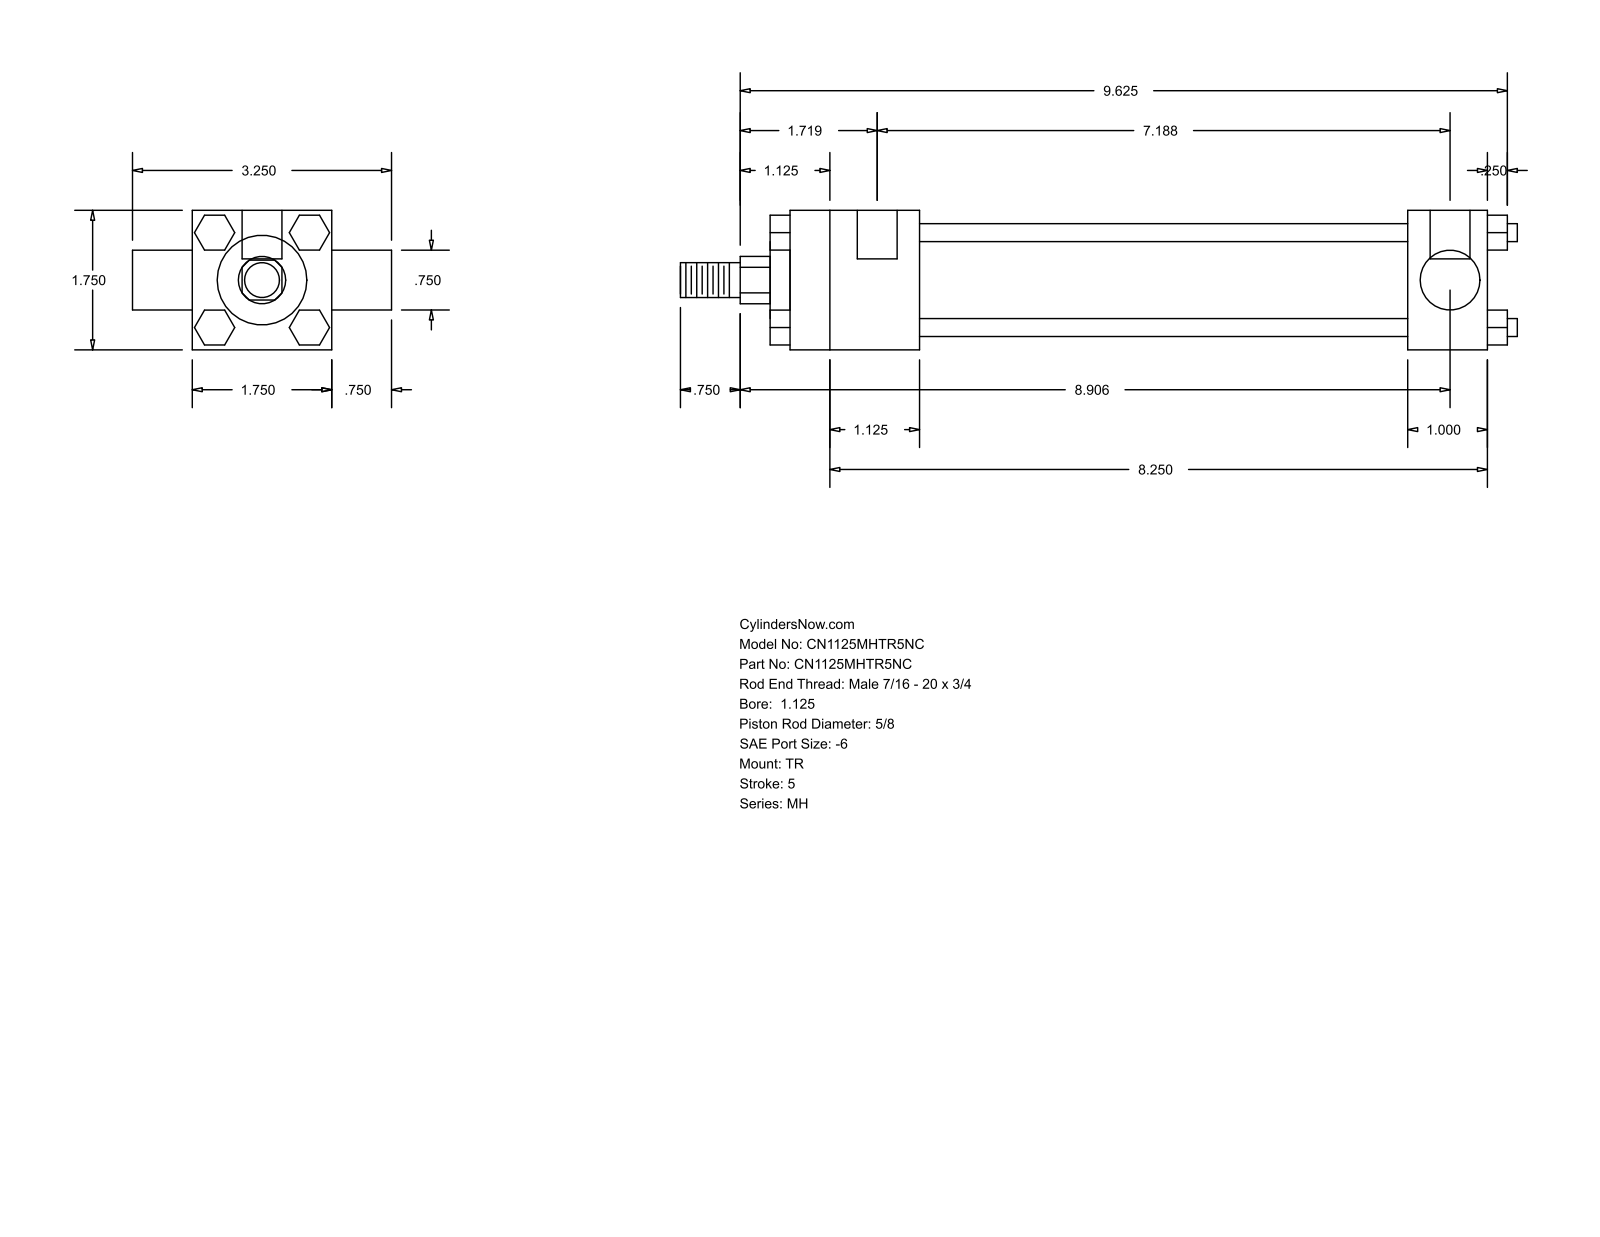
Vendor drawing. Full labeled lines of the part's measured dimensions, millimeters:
Part name (STEP PRODUCT): MH_TR__0112_0.625
STEP written by: GSSL Pune (CONFIG_CONTROL_DESIGN)
Units: millimetres
Bodies: 0 solids, 120 faces (92 planar, 28 cylindrical, 0 other)
Overall size (bounding box): 266.7 × 82.55 × 44.45
Round holes (diameter × count): ⌀5.56 ×3, ⌀12.7 ×2
Round bosses / shafts (diameter × count): ⌀5.71 ×4, ⌀34.92 ×1, ⌀28.57 ×1, ⌀19.05 ×1, ⌀15.88 ×1, ⌀11.11 ×1
Partial cylindrical surfaces — rounded edges, fillets, slot ends (radius × count): R7.54 ×1
Main face-to-face distances: 44.46, 6.35, 228.59, 11.11, 25.4, 155.57, 180.97, 41.27, 196.84, 222.24
Hole centre spacings: 3.17, 179.39, 182.56
